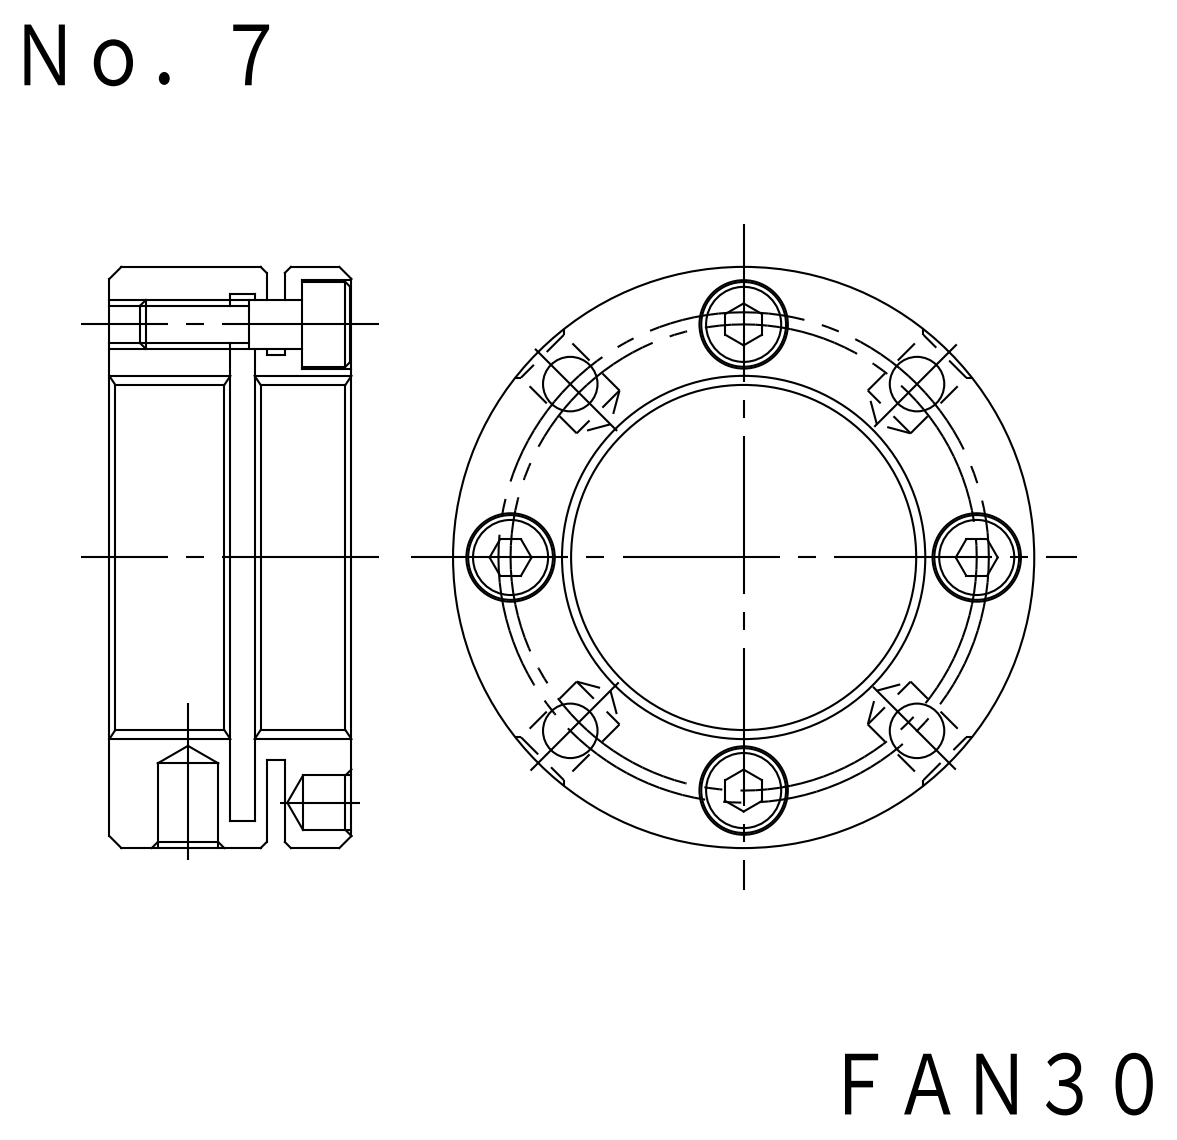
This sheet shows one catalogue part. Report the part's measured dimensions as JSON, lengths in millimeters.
{"part_name": "FKD FAN30; M4X14_default", "step_written_by": "SolidWorks 2012 (CONFIG_CONTROL_DESIGN)", "units": "millimeters", "bodies": {"solids": 5, "faces": 142, "planar": 50, "cylindrical": 76, "other": 16}, "overall_size": [48, 48, 20], "volume_mm3": 17956, "surface_area_mm2": 13177, "round_holes": [[3.24, 4], [4.3, 4], [4.5, 4], [7.3, 4], [5, 2], [30, 1], [44, 1]], "round_bosses_or_shafts": [[7, 4], [4, 4], [48, 1], [34, 1]], "face_to_face_distances": [2, 3, 20, 12.3, 7.7, 14.3, 5.7, 9.3, 5, 10.7], "hole_center_spacings": [15.23, 36.73, 19.5, 20.25, 27.58, 28.64, 39, 40.5]}
